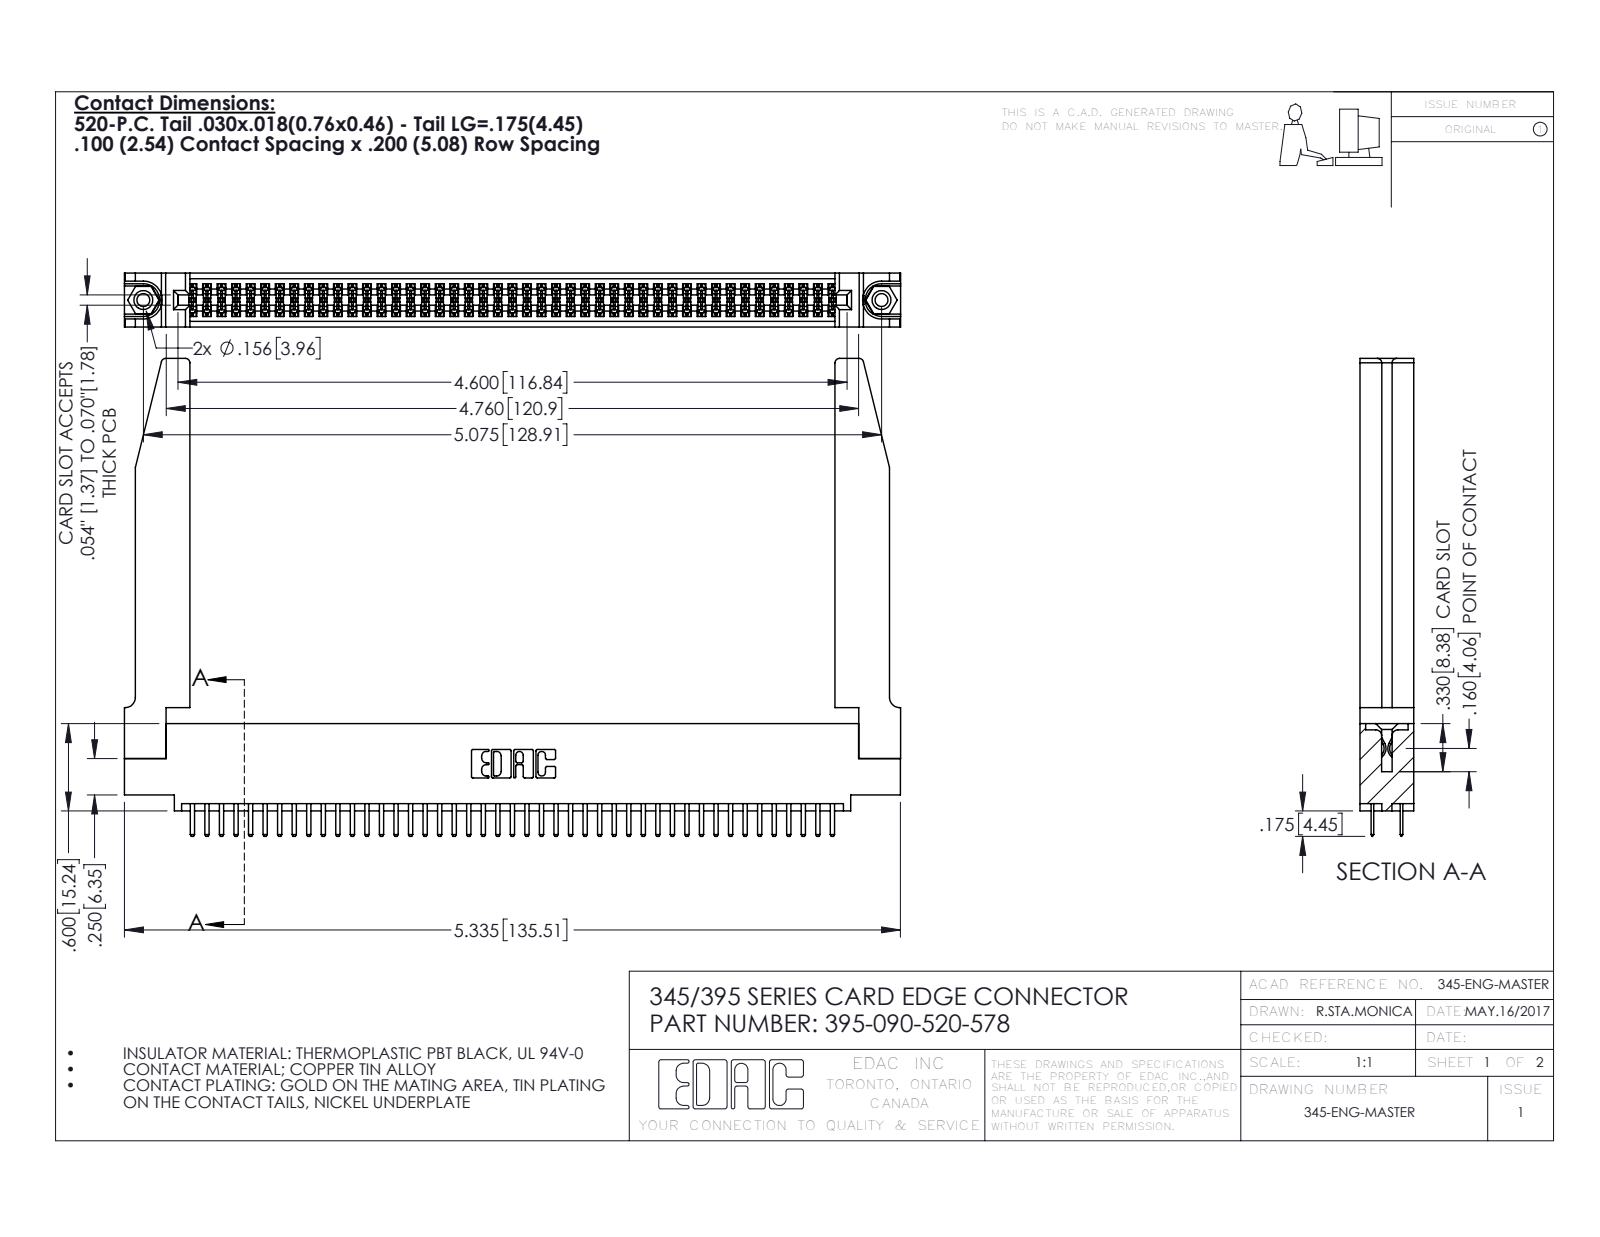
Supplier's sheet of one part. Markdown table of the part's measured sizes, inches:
| quantity | value |
| --- | --- |
| part name | 345-250-001_345-250-001-102; 395-090-520-578; 345-292-001_345-293-120; 345-220-078_345-220-078 (+1 more) |
| STEP written by | SolidWorks 2016 (CONFIG_CONTROL_DESIGN) |
| units | inches |
| bodies | 95 solids, 5224 faces (3376 planar, 1796 cylindrical, 52 other) |
| overall size | 5.336 × 3.285 × 0.37 |
| volume | 1.272 in³ |
| surface area | 40.67 in² |
| round holes (diameter × count) | 0.089 × 2, 0.125 × 2, 0.156 × 2, 0.064 × 1 |
| round bosses / shafts (diameter × count) | 0.155 × 2 |
| partial cylindrical surfaces (radius × count) | 0.006 × 135, 0.01 × 94, 0.01 × 22, 0.03 × 8, 0.007 × 6, 0.031 × 6, 0.026 × 3, 0.014 × 2 |
| main face-to-face distances | 0.37, 0.072, 0.298, 0.2, 0.098, 0.272, 0.025, 0.225, 0.022, 0.072 |
| hole center spacings | 0.27, 4.839, 5.075 |
